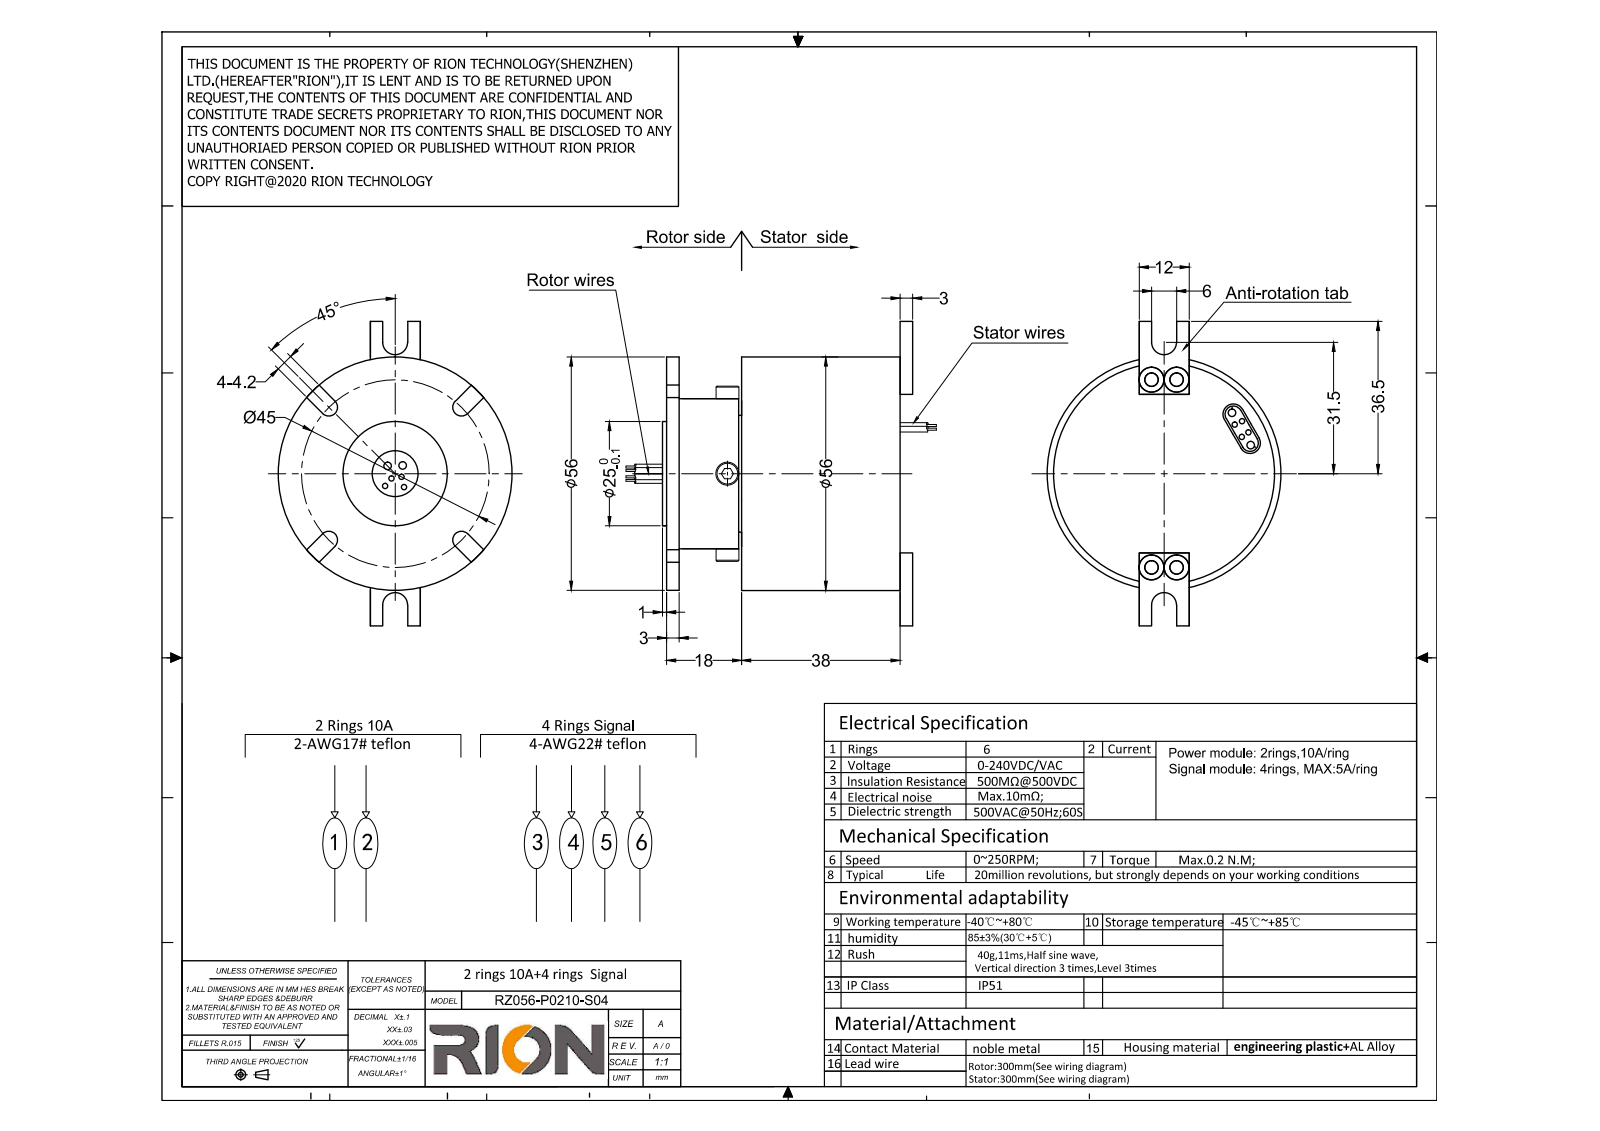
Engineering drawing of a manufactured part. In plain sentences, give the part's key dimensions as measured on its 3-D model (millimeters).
The part is named "RX00904008". Its 3-D file was written by "SolidWorks 2014 (AUTOMOTIVE_DESIGN)". It is 1 solid with 153 faces: 63 planar, 74 cylindrical and 16 other. Overall it measures 96 by 72 by 56 millimeters. Its volume is 115 537 cubic millimeters and its surface area 22 798 square millimeters. Round holes: 4 of diameter 2.5, 4 of diameter 3.2, 1 of diameter 11, 1 of diameter 53. Round bosses or shafts: 8 of diameter 1.3, 4 of diameter 1.8, 1 of diameter 56, 1 of diameter 52.9, 1 of diameter 34, 1 of diameter 28, 1 of diameter 25. Partial cylindrical surfaces (rounded edges, fillets, slot ends): 4 of radius 2.1, 2 of radius 2, 2 of radius 3. The main face-to-face distances are 56, 18, 38, 3, 15, 53, 4, 1, 19, 57. The hole center spacings are 22.2, 6, 44, 44.41.
